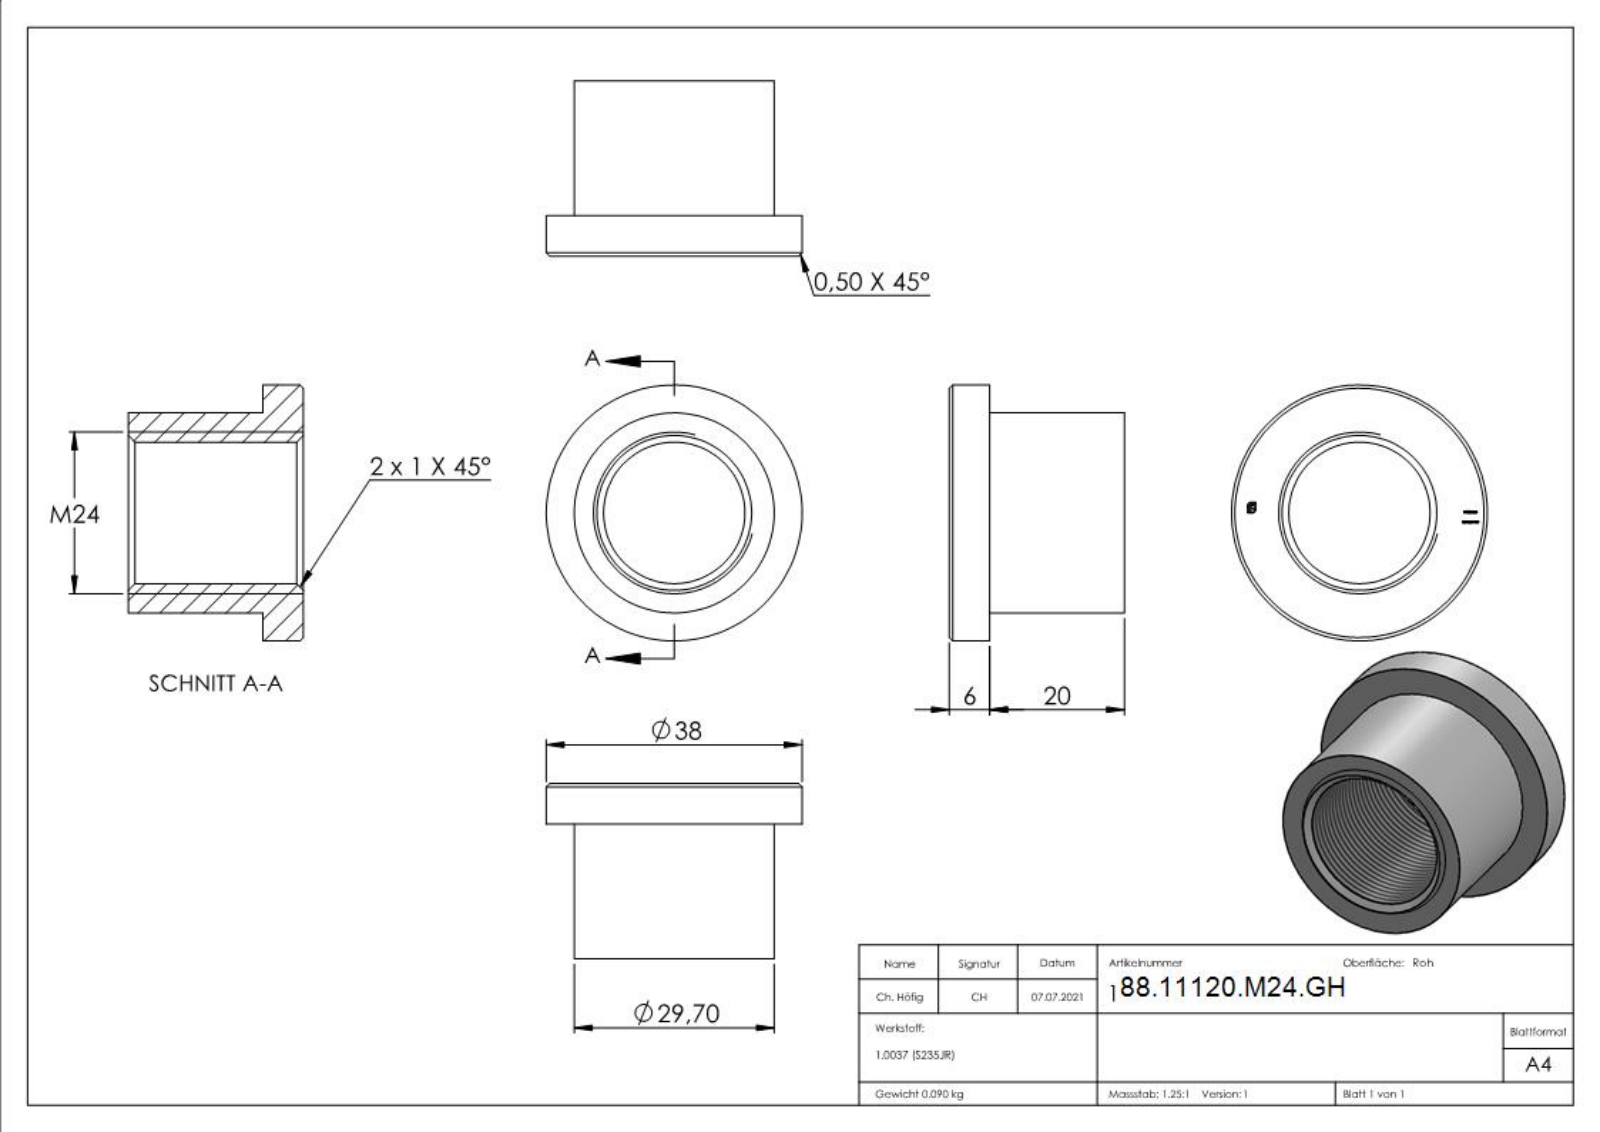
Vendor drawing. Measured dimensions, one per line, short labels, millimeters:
name: 120-M24-GH
written by: SolidWorks 2018 (CONFIG_CONTROL_DESIGN)
unit: mm
bodies: 1 solid, 281 faces (171 planar, 6 cylindrical, 104 other)
size: 38 × 38 × 26
volume: 11 572 mm³; area: 5 767 mm²
holes: 1× ⌀21
bosses: 1× ⌀38, 1× ⌀29.7
face distances: 6, 26, 20, 5.9, 25.9, 1.5, 1.47, 0.47, 1.45, 2.13
